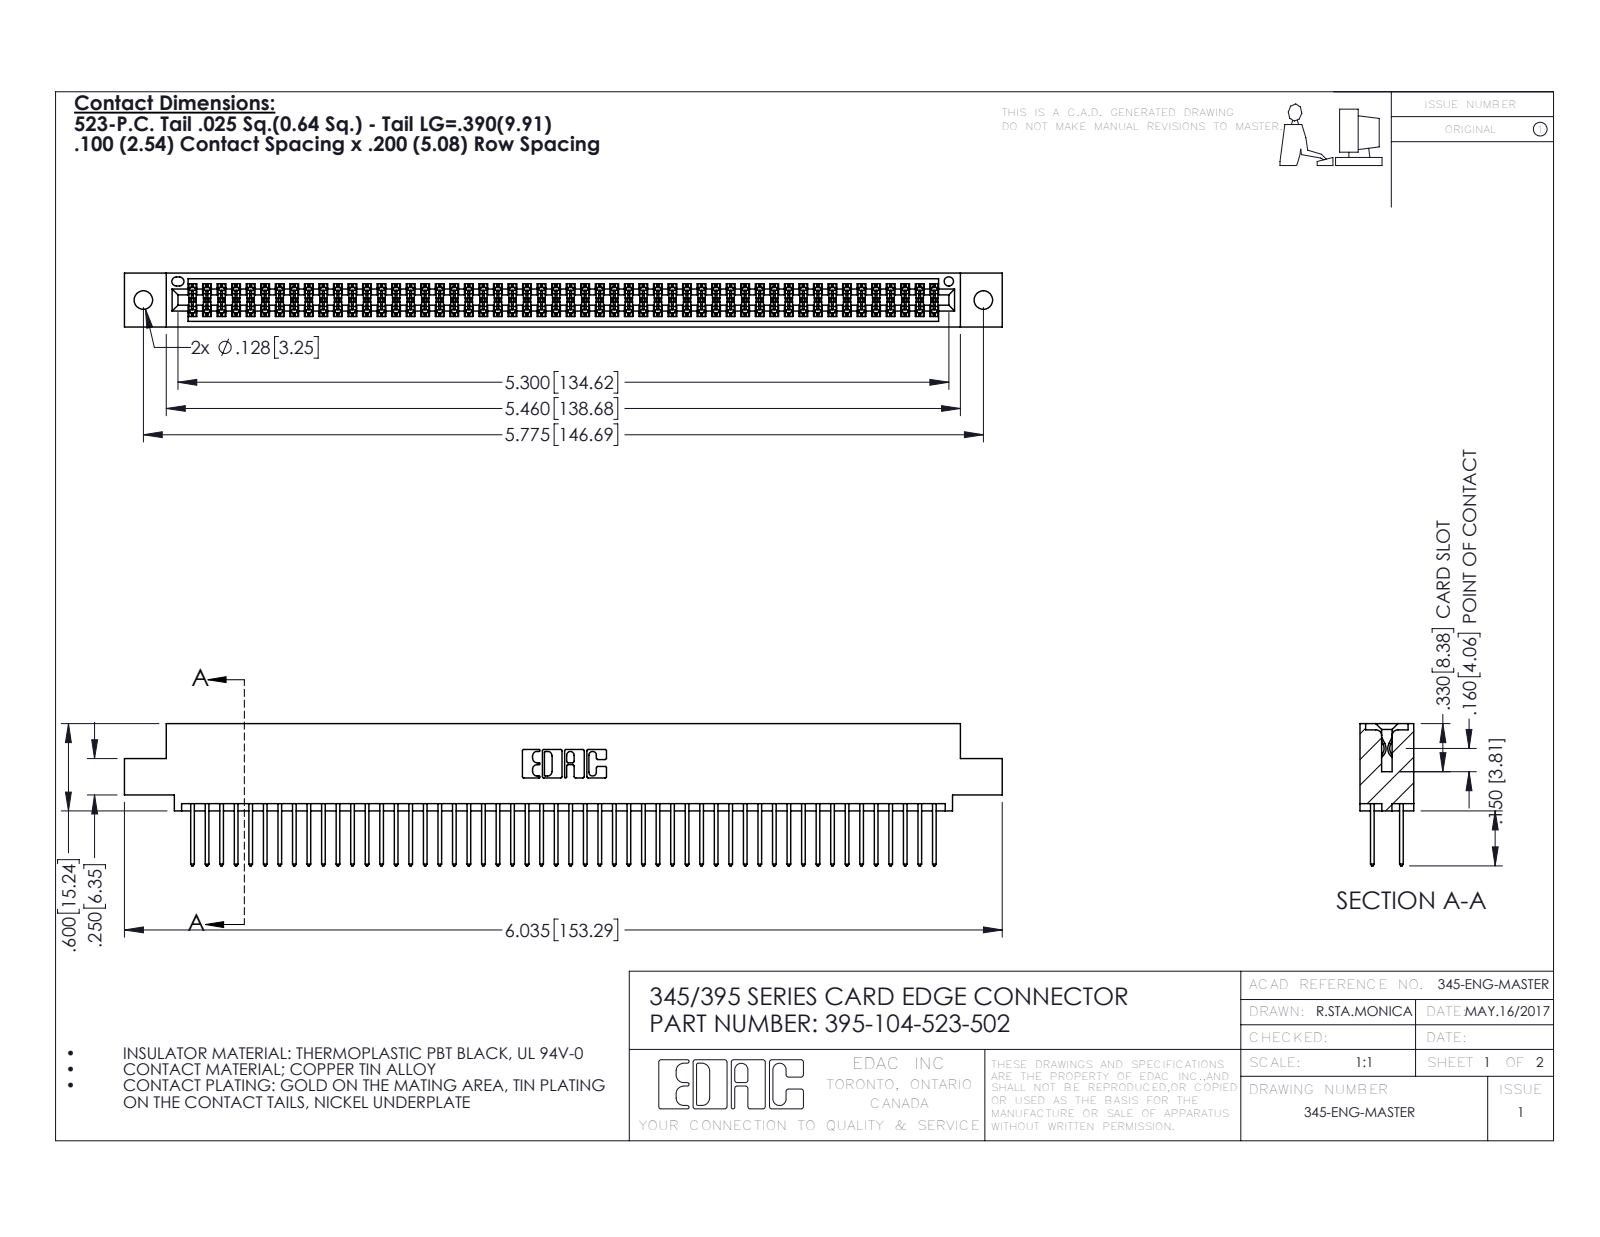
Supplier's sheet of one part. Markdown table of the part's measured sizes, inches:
| quantity | value |
| --- | --- |
| part name | 345-292-001_345-293-123; 395-104-523-502; 345 Part_0.110 Offset - 0.128 Dia |
| STEP written by | SolidWorks 2016 (CONFIG_CONTROL_DESIGN) |
| units | inches |
| bodies | 105 solids, 5330 faces (3516 planar, 1814 cylindrical, 0 other) |
| overall size | 6.035 × 0.977 × 0.37 |
| volume | 0.921 in³ |
| surface area | 36.07 in² |
| round holes (diameter × count) | 0.128 × 2, 0.064 × 1 |
| partial cylindrical surfaces (radius × count) | 0.006 × 156, 0.01 × 104, 0.01 × 22, 0.007 × 6, 0.031 × 6, 0.026 × 3, 0.014 × 2, 0.019 × 2 |
| main face-to-face distances | 0.298, 0.072, 0.2, 0.098, 0.272, 0.025, 0.37, 0.225, 0.175, 0.149 |
| hole center spacings | 0.27, 5.539, 5.775 |
